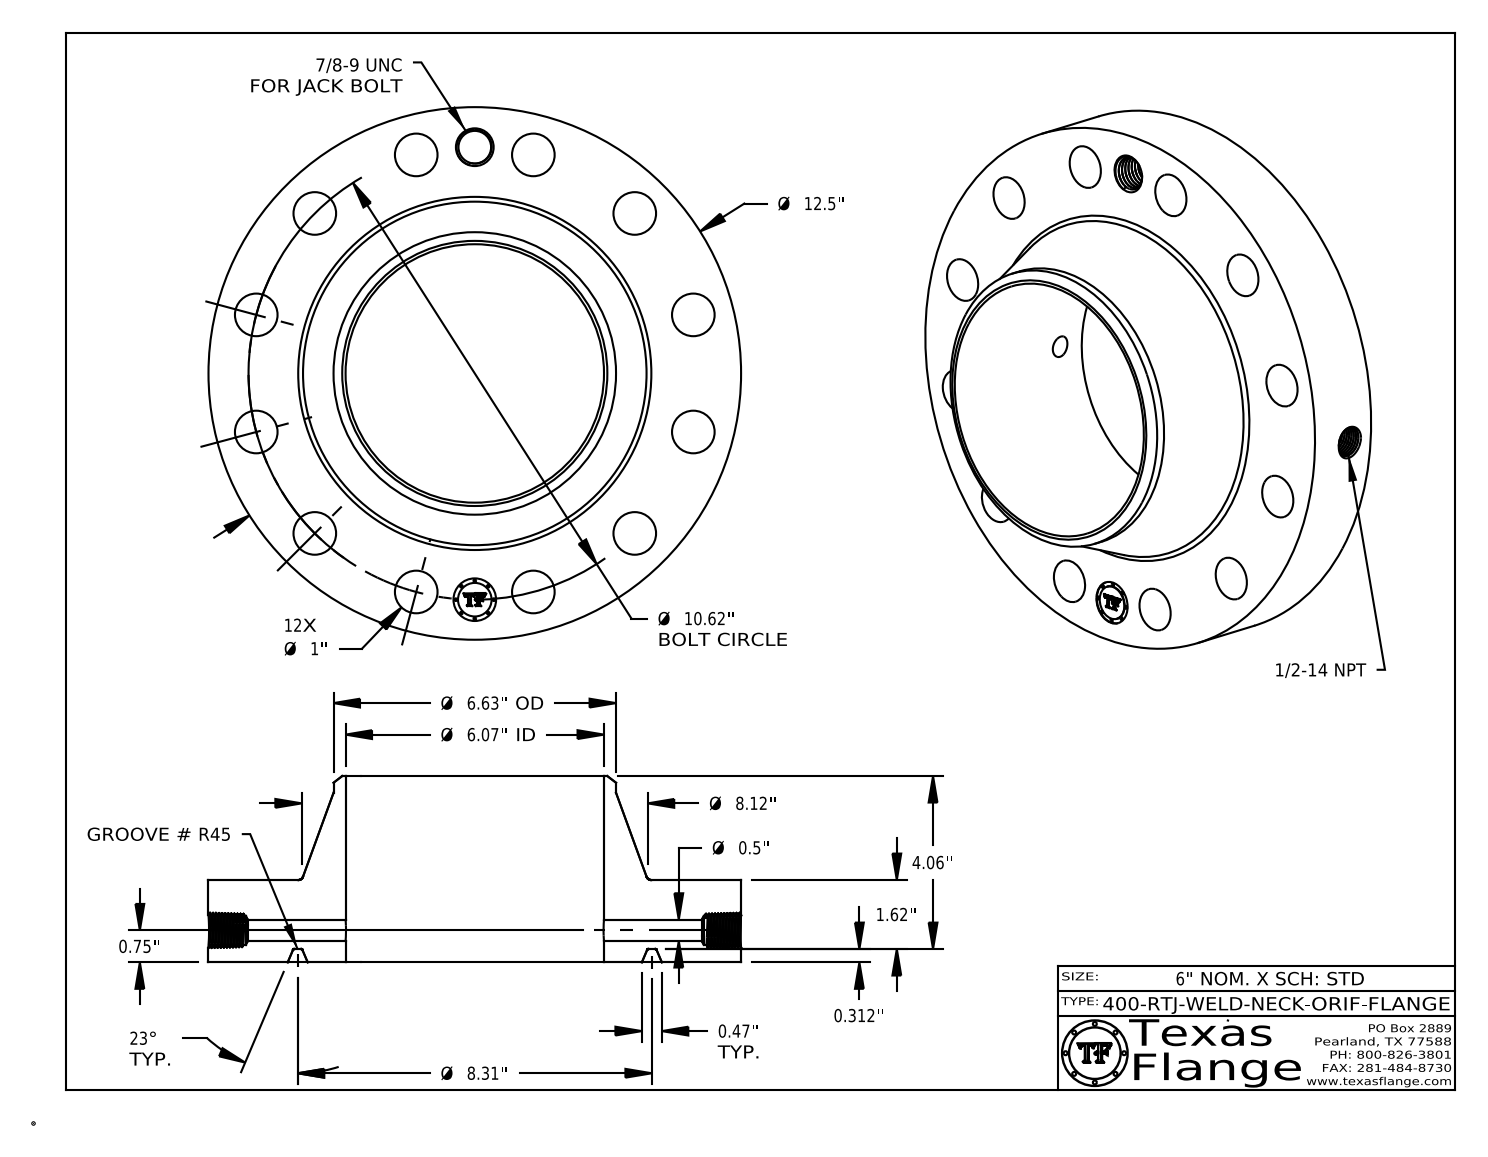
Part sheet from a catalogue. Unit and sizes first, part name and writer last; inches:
Units: inches
Overall size (bounding box): 12.5 × 12.5 × 4.372
Round holes (diameter × count): ⌀1 ×13, ⌀0.5 ×1, ⌀0.672 ×1, ⌀0.766 ×1, ⌀6.065 ×1
Round bosses / shafts (diameter × count): ⌀0.061 ×8, ⌀12.5 ×1, ⌀6.63 ×1, ⌀0.788 ×1
Main face-to-face distances: 1.932, 0.312, 1.62, 4.372, 4.06, 2.44, 0.015, 1.917, 1.605, 2.455
Hole centre spacings: 5.31, 7.509, 9.197, 10.258, 5.31, 2.748, 10.62, 1.386
Volume: 188.2 in³ · Surface area: 469.5 in²
Bodies: 1 solid, 796 faces (370 planar, 104 cylindrical, 322 other)
Part name (STEP PRODUCT): 400-RTJ-WELD-NECK
STEP written by: CATIA V5 STEP AP214 (AUTOMOTIVE_DESIGN)
